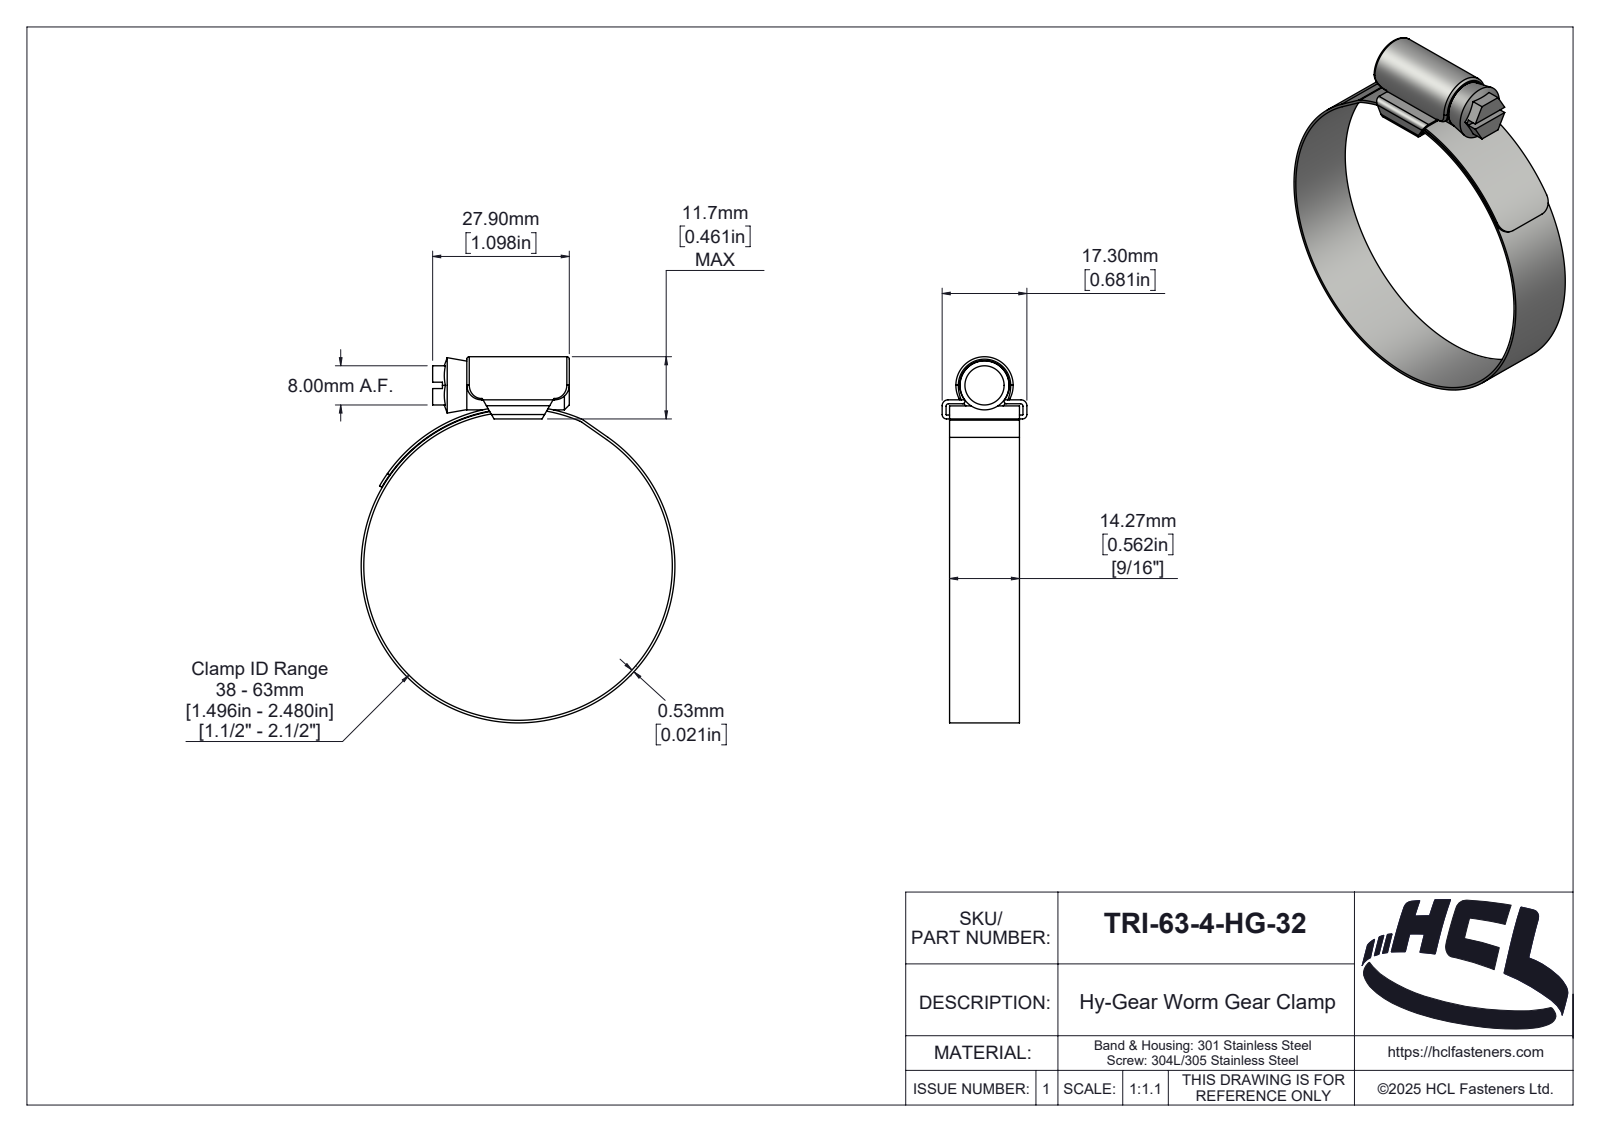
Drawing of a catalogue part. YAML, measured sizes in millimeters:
part_name: "TRI-50-0-HG-32"
step_written_by: "SolidWorks 2025 (AUTOMOTIVE_DESIGN)"
units: millimeters
bodies: {solids: 3, faces: 189, planar: 39, cylindrical: 89, other: 61}
overall_size: [74.73, 64.06, 17.3]
volume: 4559
surface_area: 9721
round_holes:
  - {diameter: 63, count: 1}
round_bosses_or_shafts:
  - {diameter: 64.06, count: 1}
  - {diameter: 10, count: 1}
partial_cylinders:
  - {radius: 0.5, count: 6}
  - {radius: 3, count: 4}
  - {radius: 0.1, count: 2}
  - {radius: 0.9, count: 2}
  - {radius: 1.2, count: 2}
  - {radius: 0.46, count: 1}
  - {radius: 1.89, count: 1}
  - {radius: 2, count: 1}
face_to_face_distances: [0.8, 3.1, 14.26, 2.3, 0.53, 3.9, 27.9, 1.52, 15.78, 16.5]
